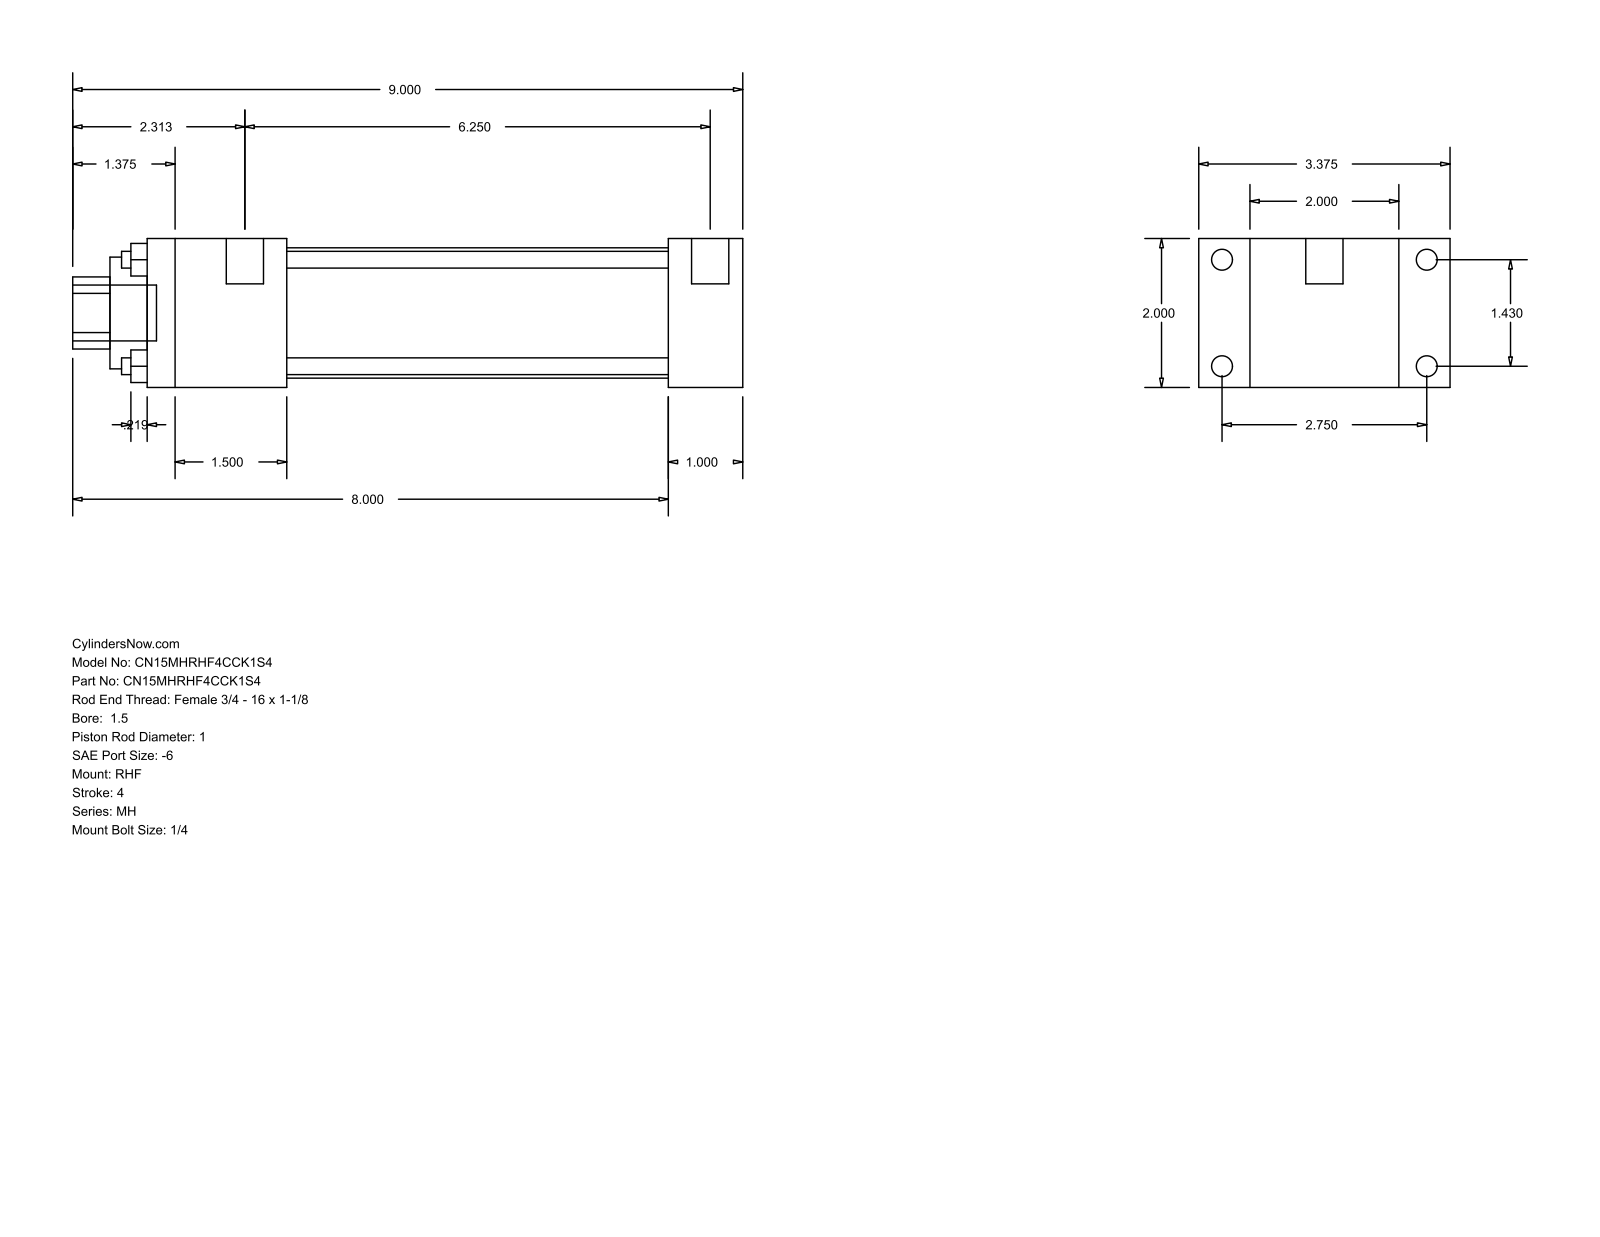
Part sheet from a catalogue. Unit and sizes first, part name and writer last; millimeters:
Units: millimetres
Overall size (bounding box): 228.6 × 85.72 × 50.8
Round holes (diameter × count): ⌀5.71 ×4, ⌀25.4 ×1, ⌀38.1 ×1, ⌀44.45 ×1
Round bosses / shafts (diameter × count): ⌀7.14 ×4, ⌀5.56 ×4, ⌀12.7 ×2, ⌀19.05 ×1
Partial cylindrical surfaces — rounded edges, fillets, slot ends (radius × count): R12.29 ×1
Main face-to-face distances: 50.8, 25.4, 17.46, 68.26, 85.72, 203.2, 177.8, 47.63, 130.17, 155.57
Hole centre spacings: 25.68, 36.32, 51.36
Bodies: 0 solids, 88 faces (60 planar, 28 cylindrical, 0 other)
Part name (STEP PRODUCT): MH_RHF__0150_1
STEP written by: GSSL Pune (CONFIG_CONTROL_DESIGN)
